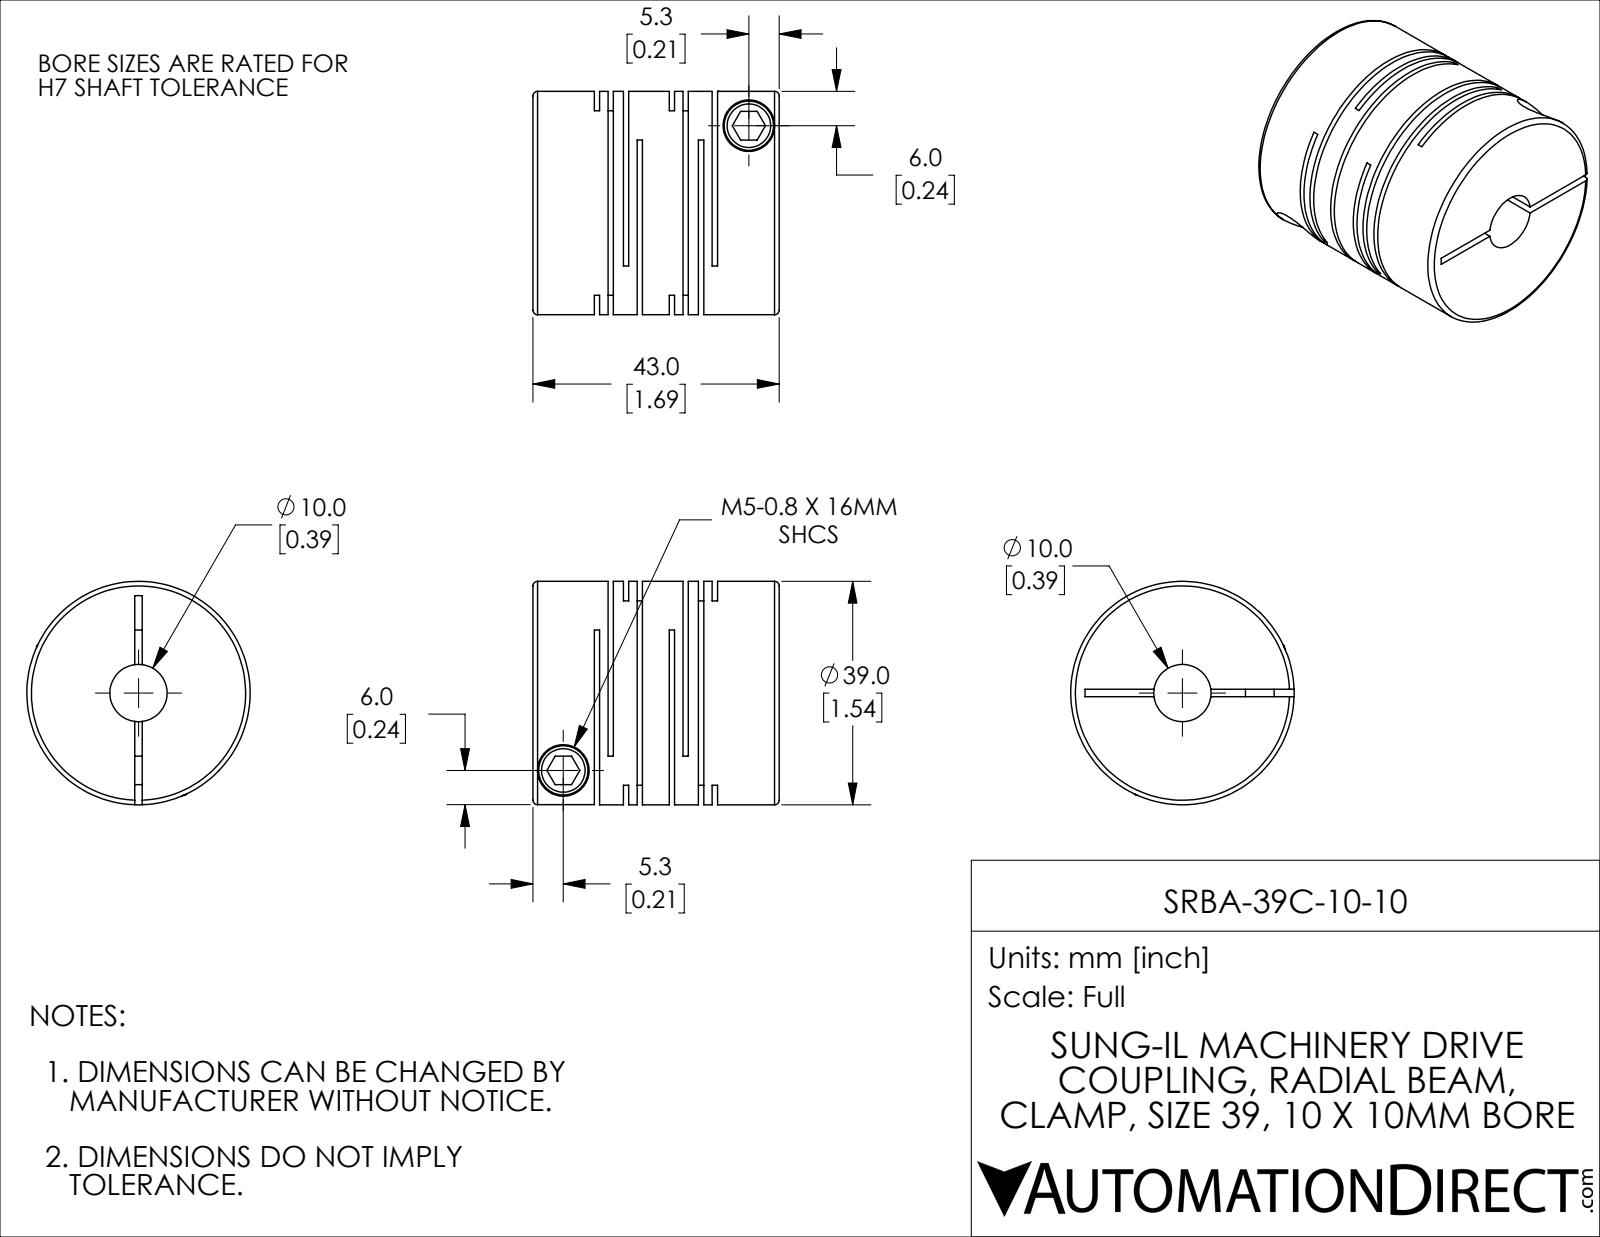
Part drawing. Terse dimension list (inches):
name: SRBA-39C-10-10
written by: SolidWorks 2021 (CONFIG_CONTROL_DESIGN)
unit: in
bodies: 1 solid, 114 faces (60 planar, 42 cylindrical, 12 other)
size: 1.693 × 1.535 × 1.535
volume: 2.413 in³; area: 38.32 in²
holes: 2× ⌀0.197, 2× ⌀0.354, 1× ⌀0.394
bosses: 2× ⌀0.339, 1× ⌀1.535
face distances: 0.516, 0.036, 0.094, 0.201, 0.421, 0.552, 0.717, 0.058, 0.48, 0.165
